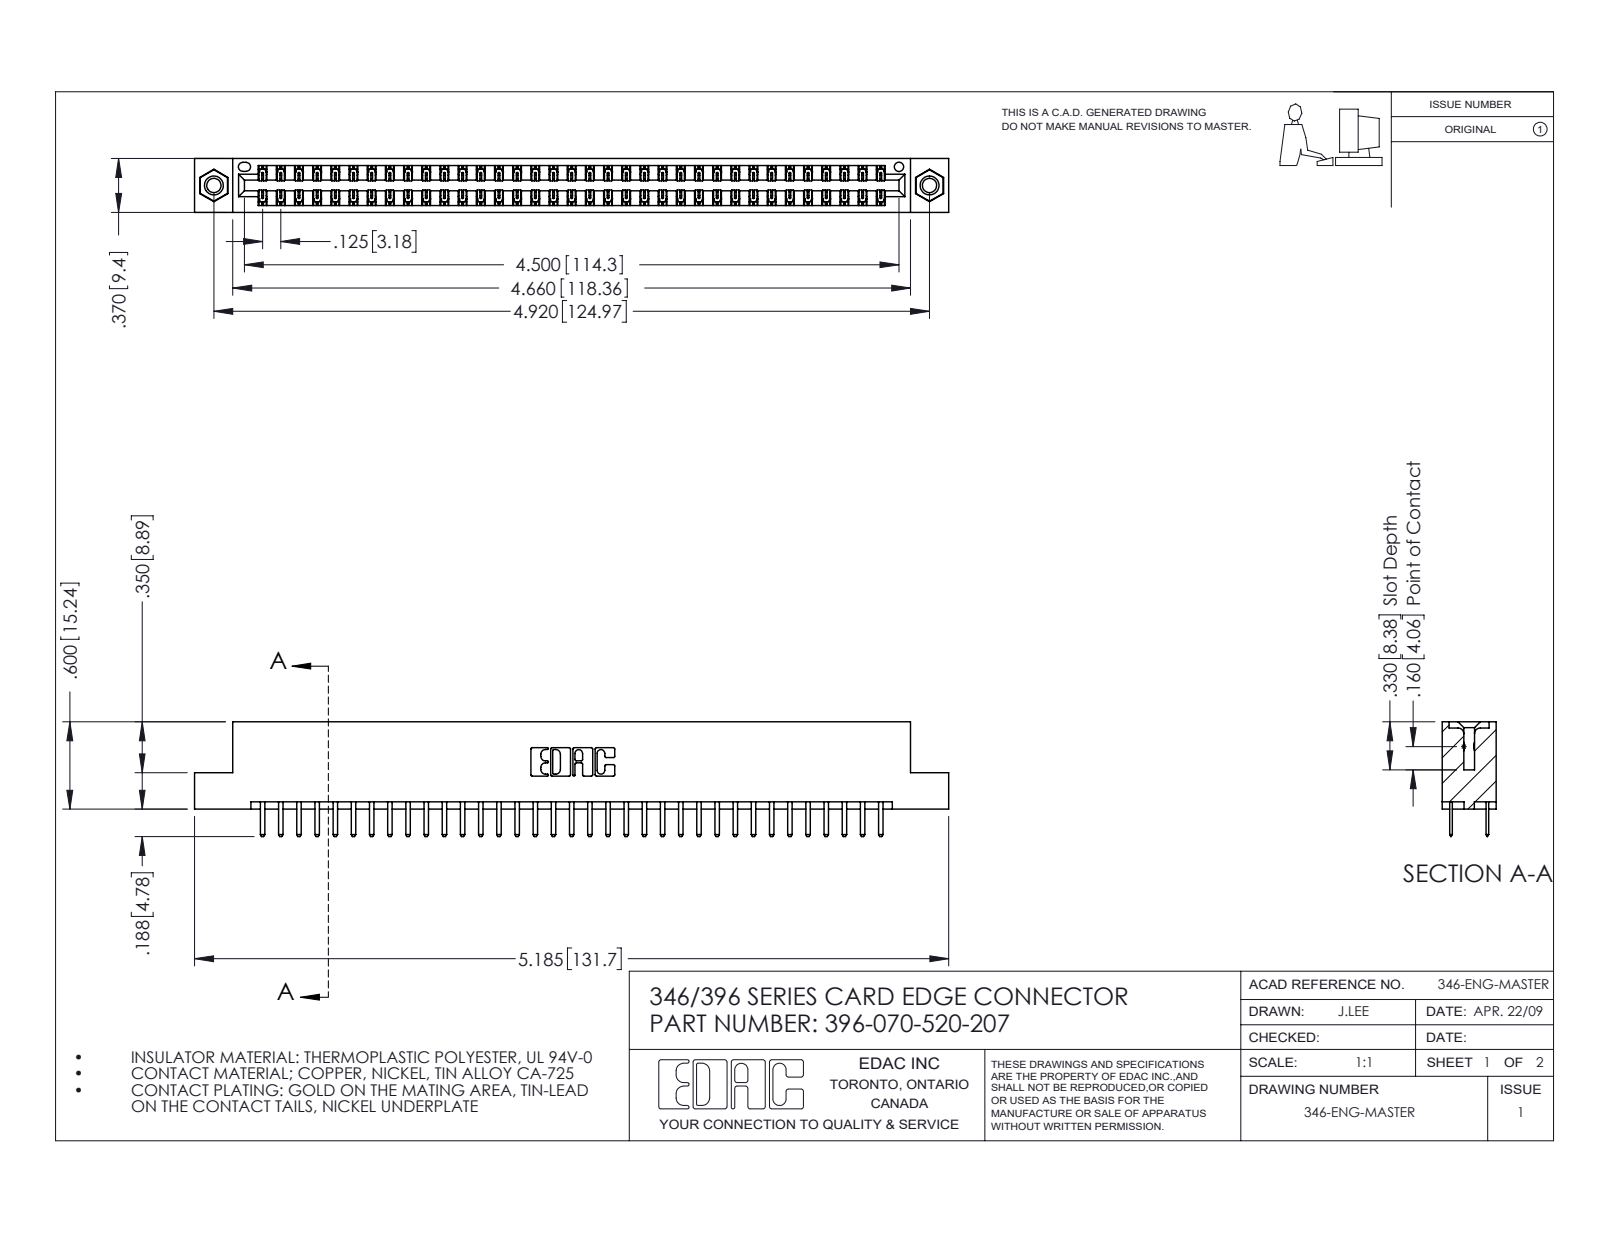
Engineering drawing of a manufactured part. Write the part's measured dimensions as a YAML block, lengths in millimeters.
part_name: "345-250-001_345-250-005-103; 396-070-520-207; 345-292-001_345-293-120; 346 Part_Flush Mounting Lugs - 0.156 Dia-TI"
step_written_by: "SolidWorks 2016 (CONFIG_CONTROL_DESIGN)"
units: millimeters
bodies: {solids: 73, faces: 4102, planar: 2698, cylindrical: 1388, other: 16}
overall_size: [131.7, 20, 9.4]
volume: 12700
surface_area: 17370
round_holes:
  - {diameter: 2.5, count: 2}
  - {diameter: 3.2, count: 2}
  - {diameter: 4, count: 2}
  - {diameter: 1.6, count: 1}
round_bosses_or_shafts:
  - {diameter: 3.9, count: 2}
partial_cylinders:
  - {radius: 0.2, count: 105}
  - {radius: 0.3, count: 74}
  - {radius: 0.3, count: 22}
  - {radius: 0.2, count: 6}
  - {radius: 0.8, count: 6}
  - {radius: 0.7, count: 3}
  - {radius: 0.4, count: 2}
  - {radius: 0.6, count: 2}
face_to_face_distances: [1.2, 8.2, 6.4, 9.4, 7, 1.8, 7.6, 0.6, 3.8, 5.6]
hole_center_spacings: [6.2, 119.7, 125]
